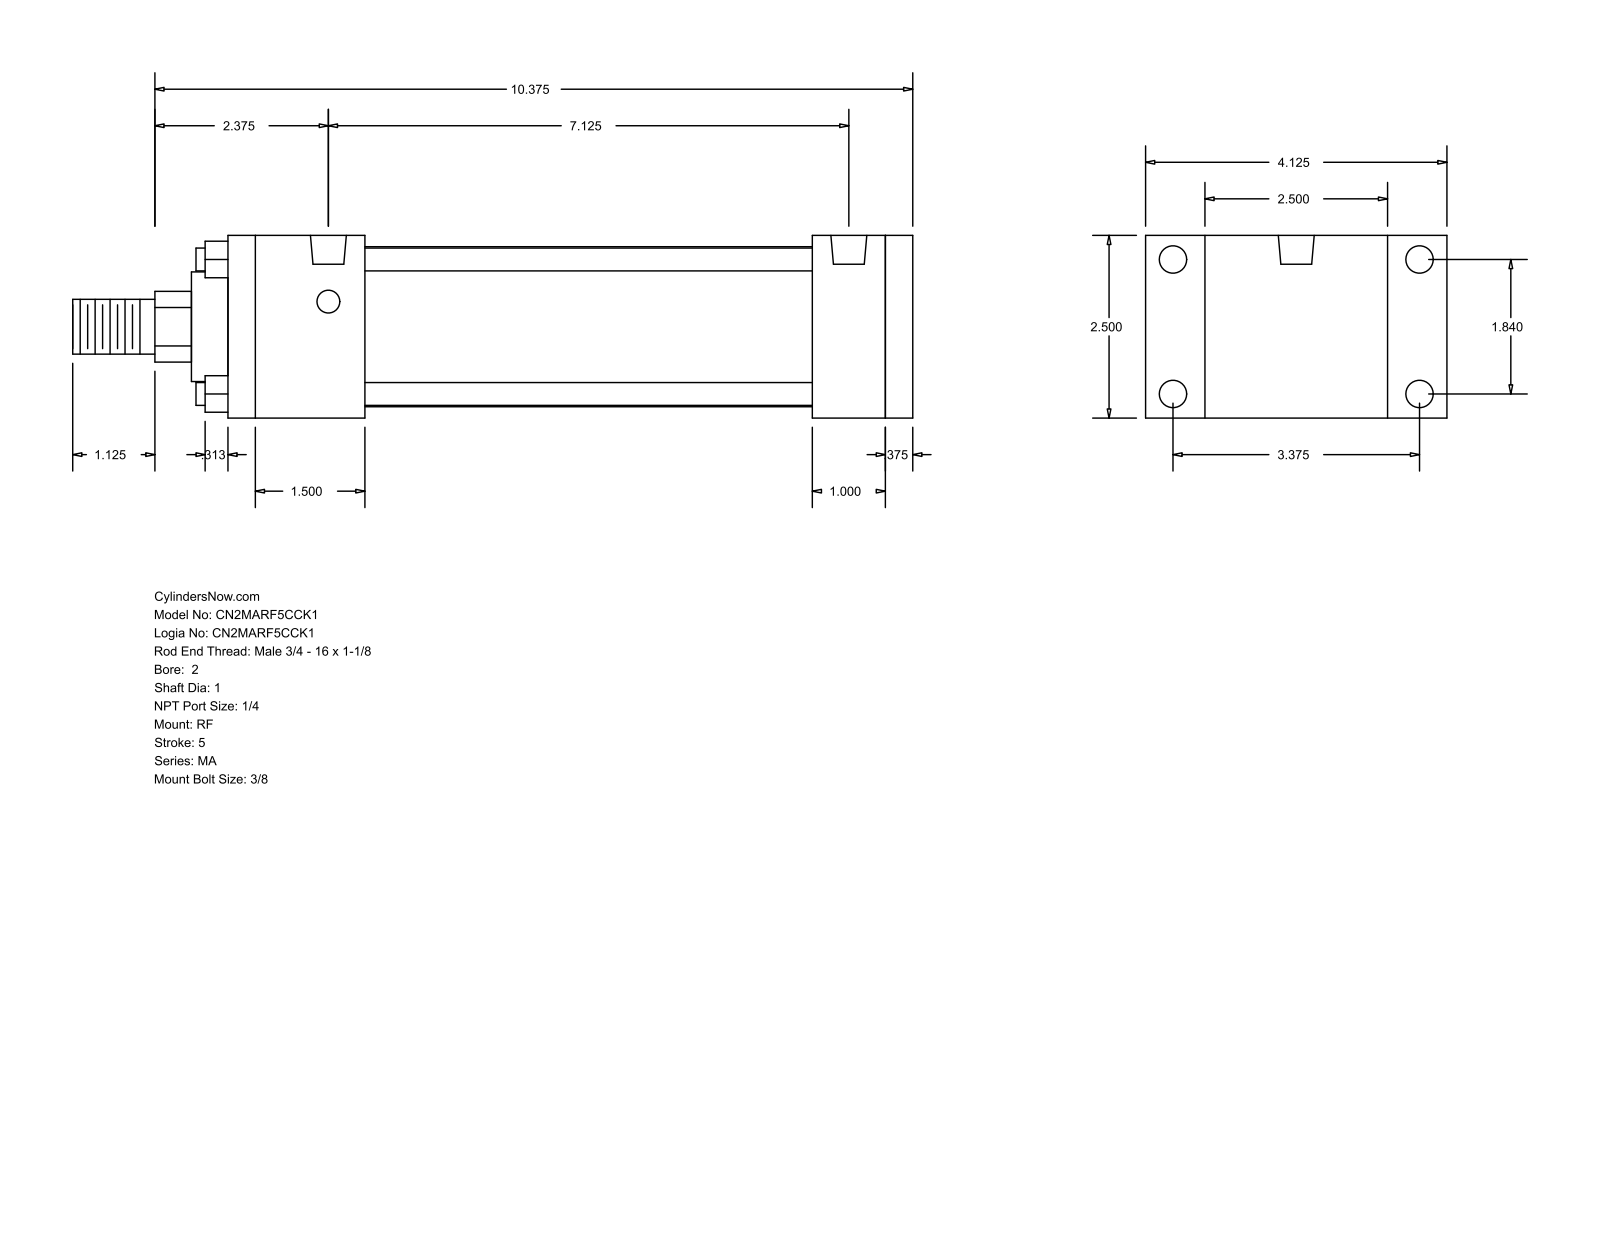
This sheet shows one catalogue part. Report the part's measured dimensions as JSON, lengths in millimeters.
{"part_name": "MA_RF__0200_1", "step_written_by": "GSSL Pune (CONFIG_CONTROL_DESIGN)", "units": "millimeters", "bodies": {"solids": 0, "faces": 92, "planar": 64, "cylindrical": 28, "other": 0}, "overall_size": [292.1, 104.78, 63.5], "round_holes": [[7.94, 4], [9.53, 4], [12.49, 2]], "round_bosses_or_shafts": [[7.94, 4], [55.63, 1], [38.1, 1], [25.4, 1], [19.05, 1]], "partial_cylinders_radius": [[12.29, 1]], "face_to_face_distances": [63.5, 228.6, 9.52, 238.12, 25.4, 20.64, 12.7, 47.63, 180.97, 190.49], "hole_center_spacings": [46.74, 85.72, 97.63, 180.97]}
